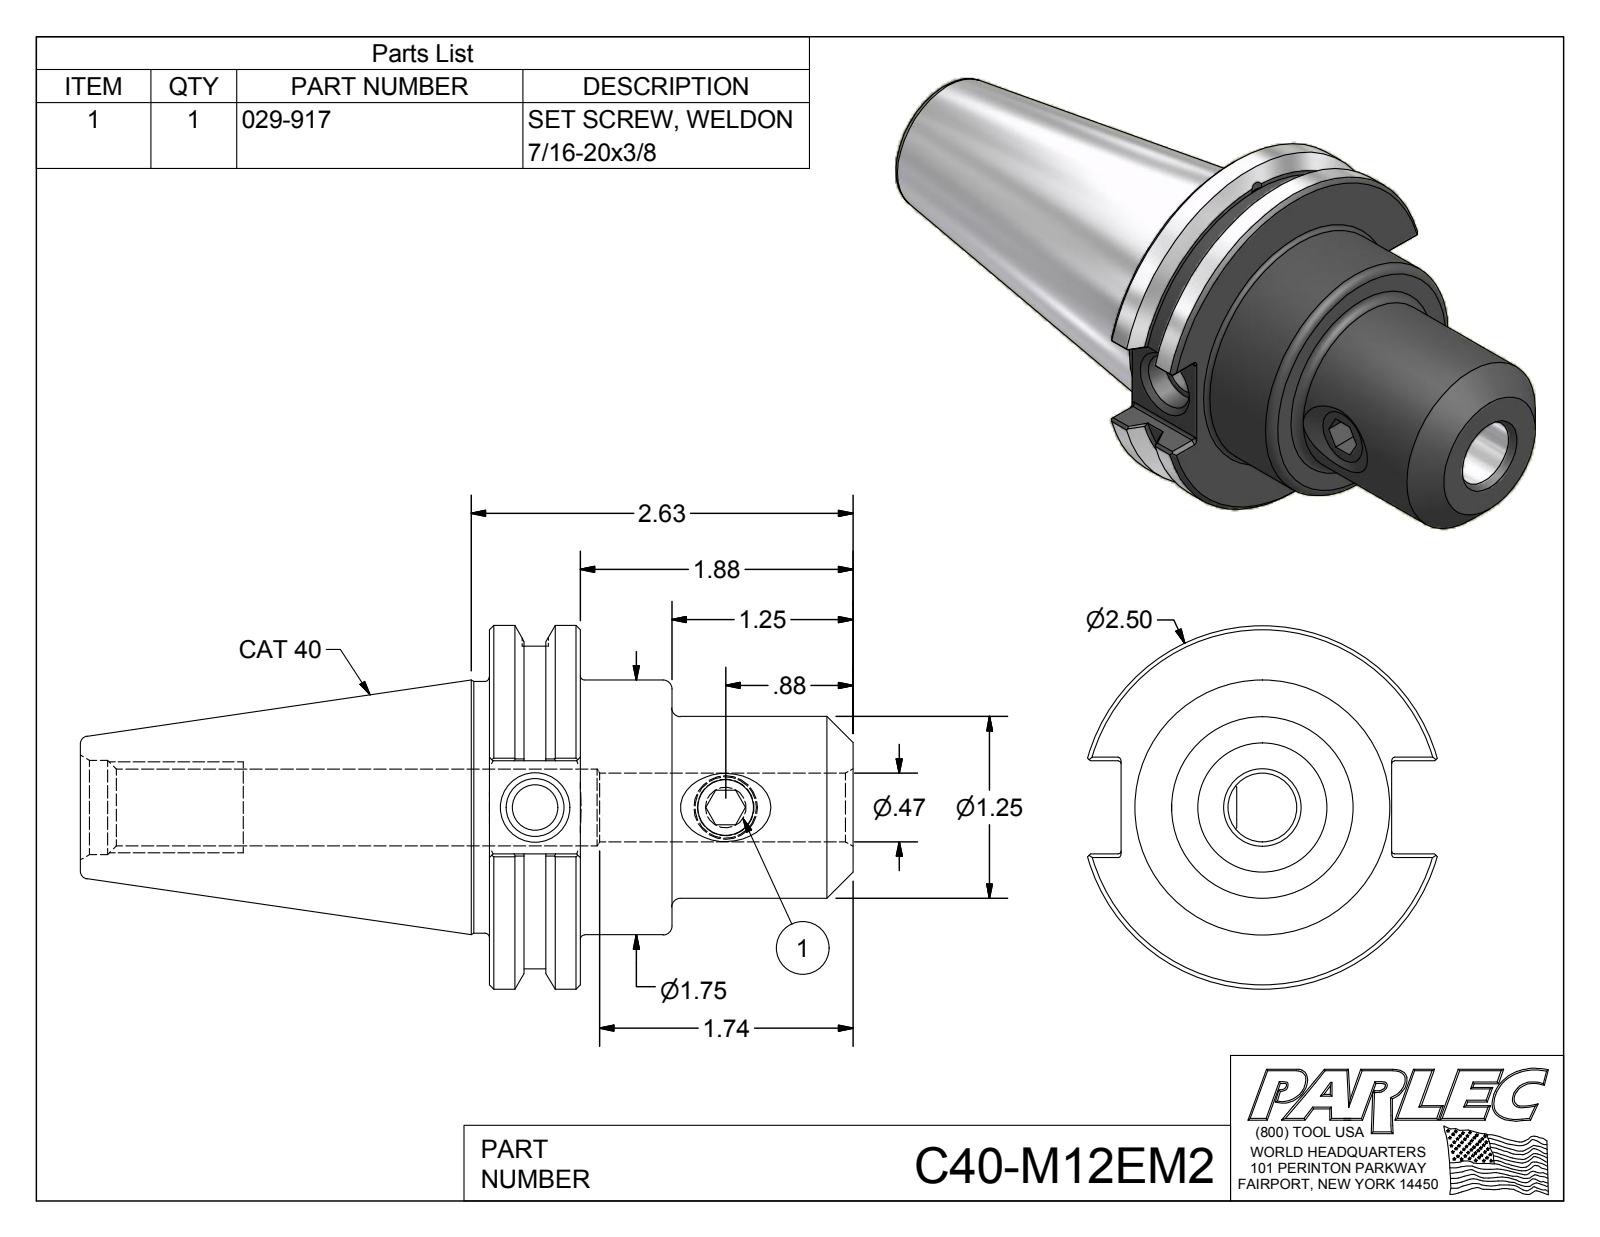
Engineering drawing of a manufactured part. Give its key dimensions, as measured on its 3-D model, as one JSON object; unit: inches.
{"part_name": "C40-M12EM2; C40-M12EM2-1; 029-917", "step_written_by": "Autodesk Inventor 2012 (AUTOMOTIVE_DESIGN)", "units": "inches", "bodies": {"solids": 2, "faces": 108, "planar": 45, "cylindrical": 30, "other": 33}, "overall_size": [5.749, 2.5, 2.406], "volume_in3": 8.761, "surface_area_in2": 42.91, "round_holes": [[0.315, 1], [0.383, 1], [0.399, 1], [0.472, 1], [0.527, 1], [0.648, 1]], "round_bosses_or_shafts": [[2.5, 1], [2.219, 1], [1.75, 1], [1.73, 1], [1.25, 1], [0.437, 1]], "partial_cylinders_radius": [[0.02, 12], [0.09, 1]], "face_to_face_distances": [0.625, 1.255, 0.63, 2.5, 1.875, 1.245, 0.236, 0.64, 1.86, 2.812], "hole_center_spacings": [1.31]}
